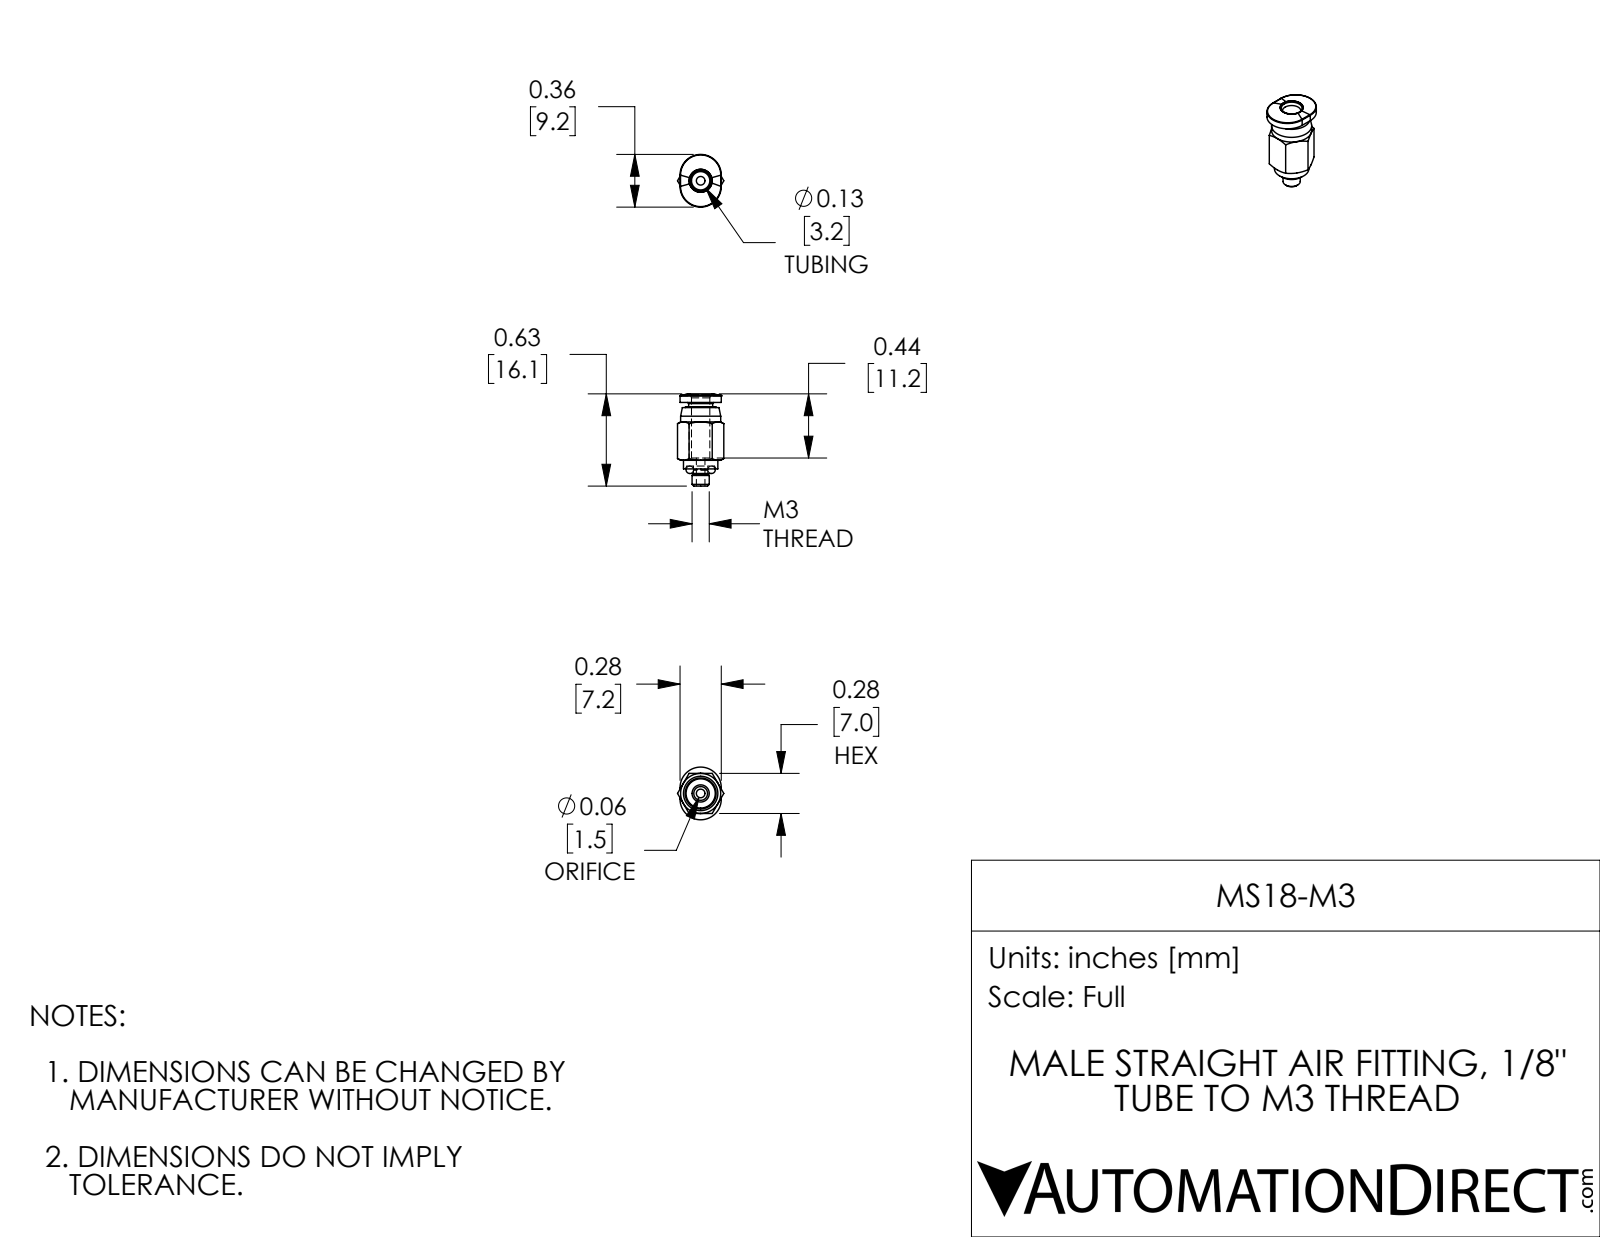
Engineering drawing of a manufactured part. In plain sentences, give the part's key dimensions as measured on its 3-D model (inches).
The part is named "MS18-M3". Its 3-D file was written by "SolidWorks 2017 (AUTOMOTIVE_DESIGN)". It is 2 solids with 83 faces: 18 planar, 21 cylindrical and 44 other. Overall it measures 0.634 by 0.362 by 0.318 inches. Its volume is 0.026 cubic inches and its surface area 1.024 square inches. Round holes: 1 of diameter 0.059, 1 of diameter 0.126. Round bosses or shafts: 1 of diameter 0.276, 1 of diameter 0.236, 1 of diameter 0.209, 1 of diameter 0.165, 1 of diameter 0.118, 1 of diameter 0.098. Partial cylindrical surfaces (rounded edges, fillets, slot ends): 2 of radius 0.142. The main face-to-face distances are 0.276, 0.437, 0.039, 0.398, 0.402, 0.362, 0.035, 0.407, 0.368, 0.03.
